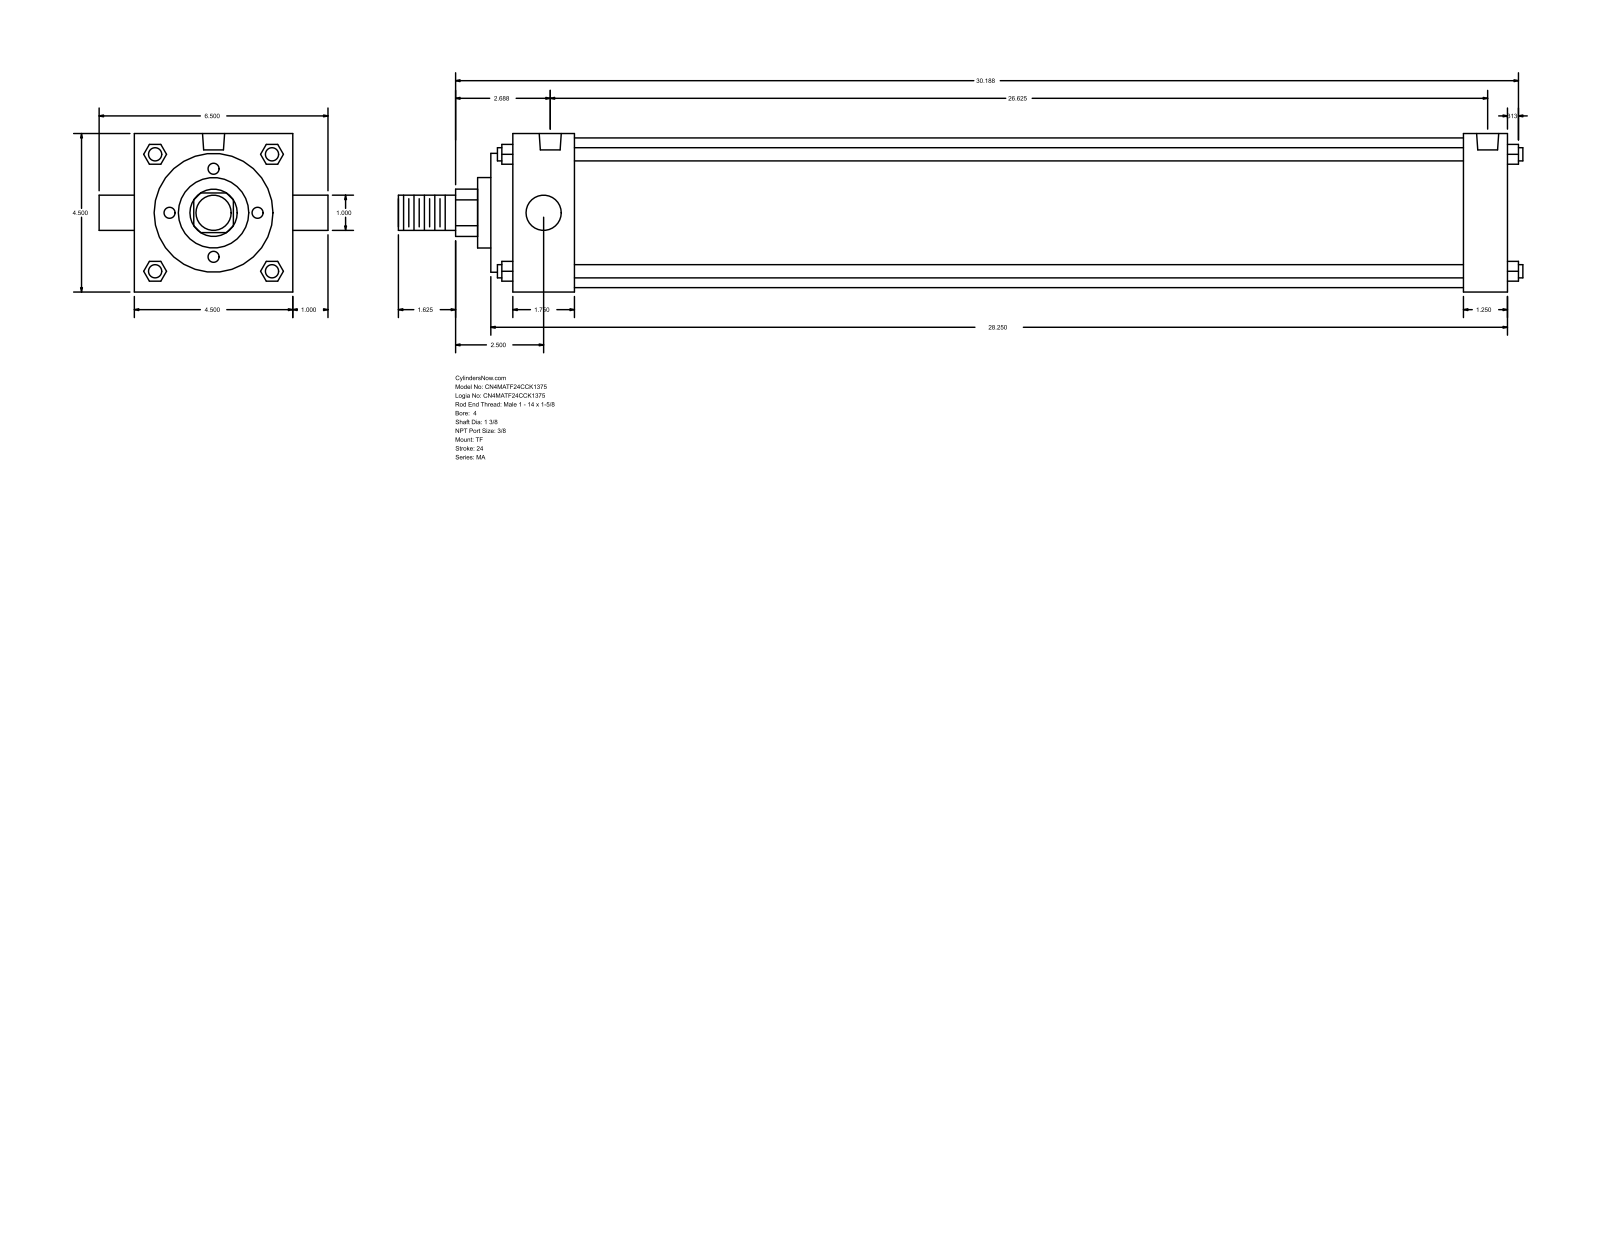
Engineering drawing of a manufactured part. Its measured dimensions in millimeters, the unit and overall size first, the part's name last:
Units: millimetres
Overall size (bounding box): 811.21 × 165.1 × 114.3
Round holes (diameter × count): ⌀11.11 ×3, ⌀15.93 ×2
Round bosses / shafts (diameter × count): ⌀9.53 ×4, ⌀25.4 ×2, ⌀107.95 ×1, ⌀85.72 ×1, ⌀50.8 ×1, ⌀34.92 ×1
Partial cylindrical surfaces — rounded edges, fillets, slot ends (radius × count): R17.06 ×1
Main face-to-face distances: 114.3, 717.56, 15.87, 733.43, 701.68, 685.81, 31.75, 60.32, 44.45, 641.36
Hole centre spacings: 4.77, 671.51, 666.74, 676.28
Bodies: 0 solids, 122 faces (93 planar, 29 cylindrical, 0 other)
Part name (STEP PRODUCT): MA_TF__0400_1.375
STEP written by: GSSL Pune (CONFIG_CONTROL_DESIGN)
